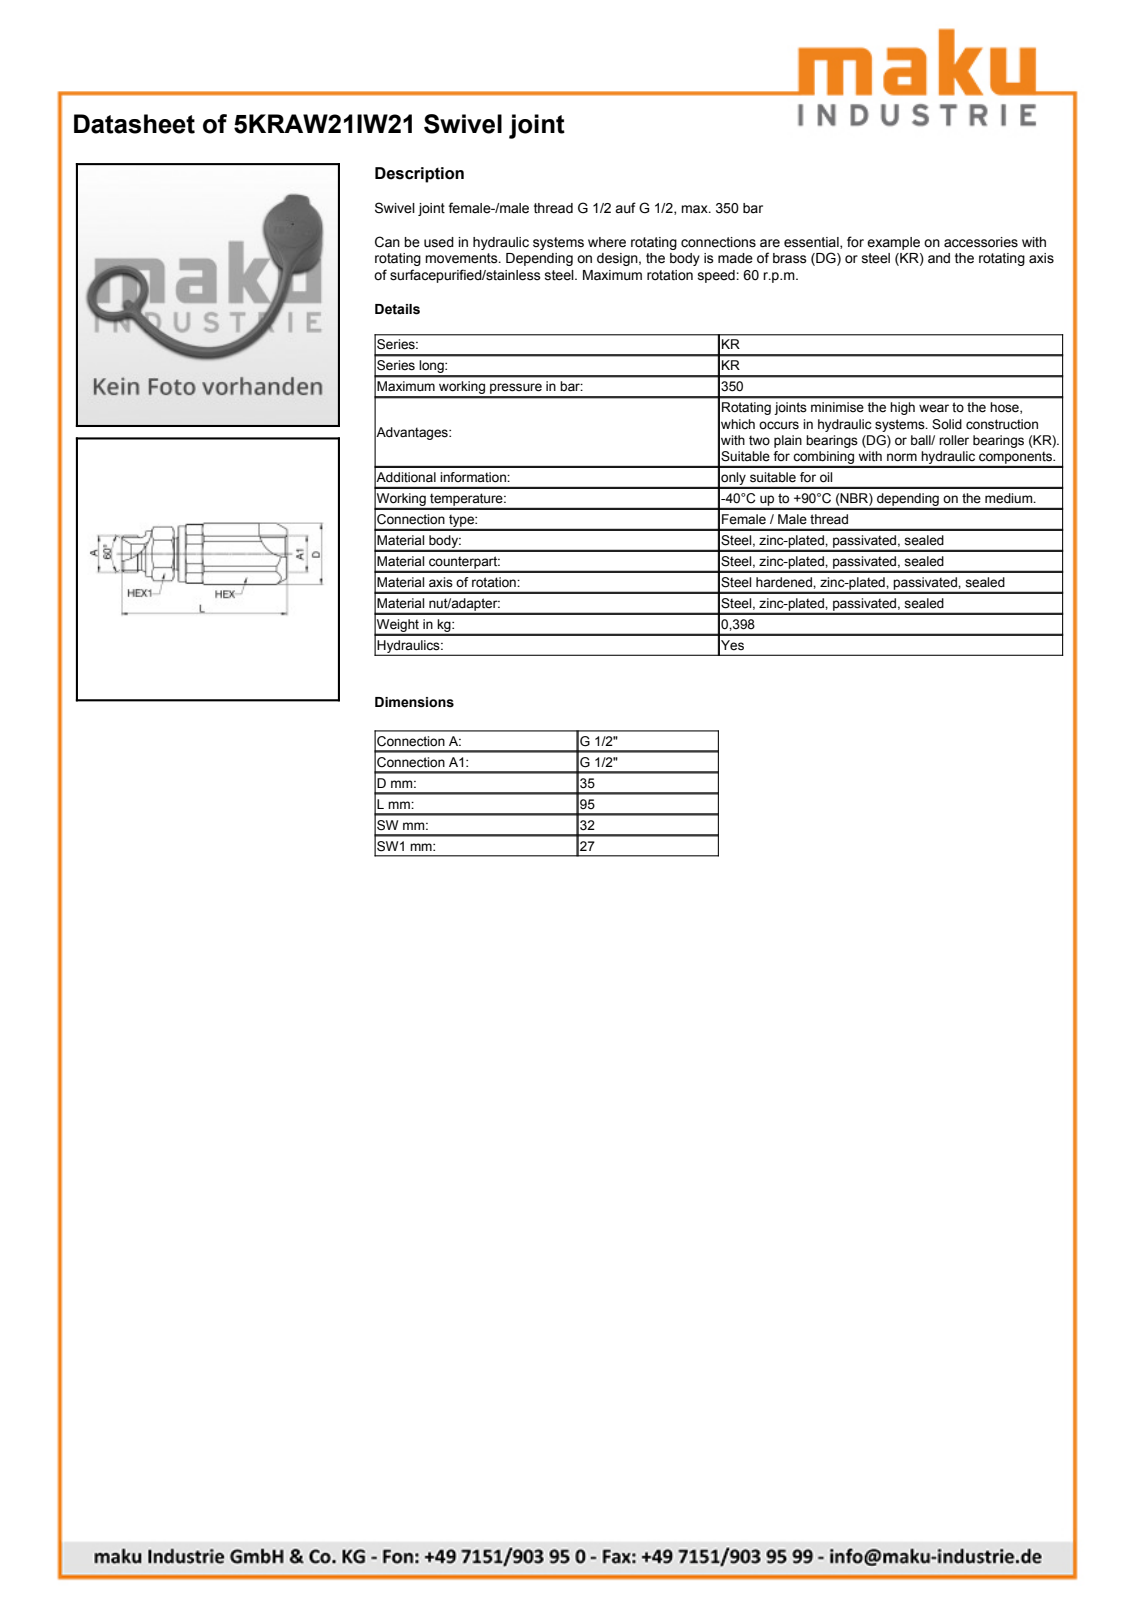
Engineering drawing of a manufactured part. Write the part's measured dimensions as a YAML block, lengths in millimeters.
part_name: "5KRAW21IW21"
step_written_by: "SolidWorks 2009 (AUTOMOTIVE_DESIGN)"
units: millimeters
bodies: {solids: 1, faces: 181, planar: 41, cylindrical: 53, other: 87}
overall_size: [95.05, 35, 32]
volume: 54876
surface_area: 16740
round_holes:
  - {diameter: 11.3, count: 1}
  - {diameter: 11.7, count: 1}
  - {diameter: 16.3, count: 1}
  - {diameter: 18.4, count: 1}
  - {diameter: 18.7, count: 1}
  - {diameter: 23.6, count: 1}
  - {diameter: 24, count: 1}
  - {diameter: 30.2, count: 1}
round_bosses_or_shafts:
  - {diameter: 31.7, count: 1}
  - {diameter: 30, count: 1}
  - {diameter: 26, count: 1}
  - {diameter: 20.95, count: 1}
  - {diameter: 17.9, count: 1}
  - {diameter: 17.4, count: 1}
  - {diameter: 16, count: 1}
partial_cylinders:
  - {radius: 17, count: 1}
  - {radius: 17.5, count: 1}
face_to_face_distances: [32, 2.5, 29.5, 27, 1.85, 63.2, 65.05, 11, 21, 8.5]
